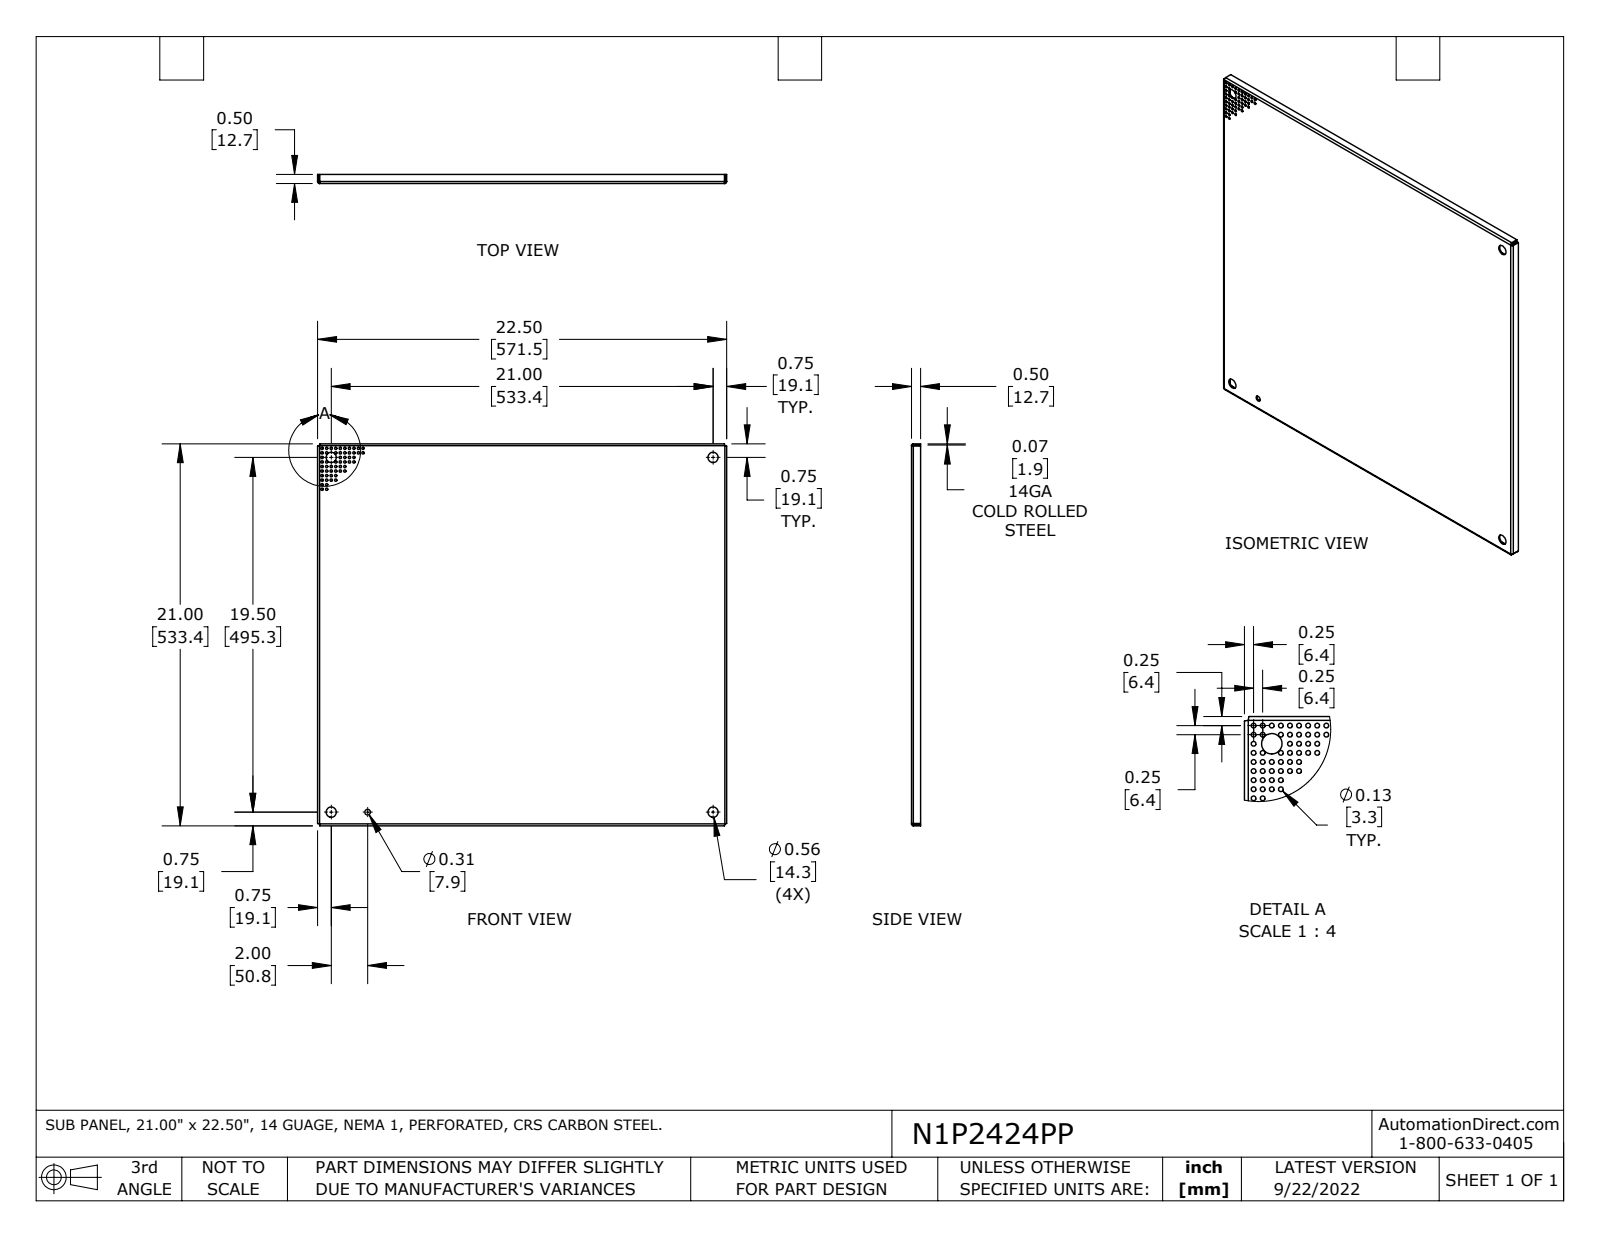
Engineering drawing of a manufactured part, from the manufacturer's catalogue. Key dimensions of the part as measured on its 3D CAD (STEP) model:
Part name (STEP PRODUCT): N1P2424PP
STEP written by: SolidWorks 2021 (AUTOMOTIVE_DESIGN)
Units: inches
Bodies: 1 solid, 158 faces (22 planar, 128 cylindrical, 8 other)
Overall size (bounding box): 22.5 × 21 × 0.5
Volume: 37.35 in³ · Surface area: 1 018 in²
Round holes (diameter × count): ⌀0.13 ×55, ⌀0.563 ×4, ⌀0.312 ×1
Partial cylindrical surfaces — rounded edges, fillets, slot ends (radius × count): R0.031 ×4, R0.105 ×4
Main face-to-face distances: 0.074, 20.926, 22.426, 20.852, 21, 22.5, 22.352, 0.426, 0.5, 0.126
Hole centre spacings: 0.25, 1.25, 0.559, 0.354, 0.791, 0.5, 1.031, 0.75
